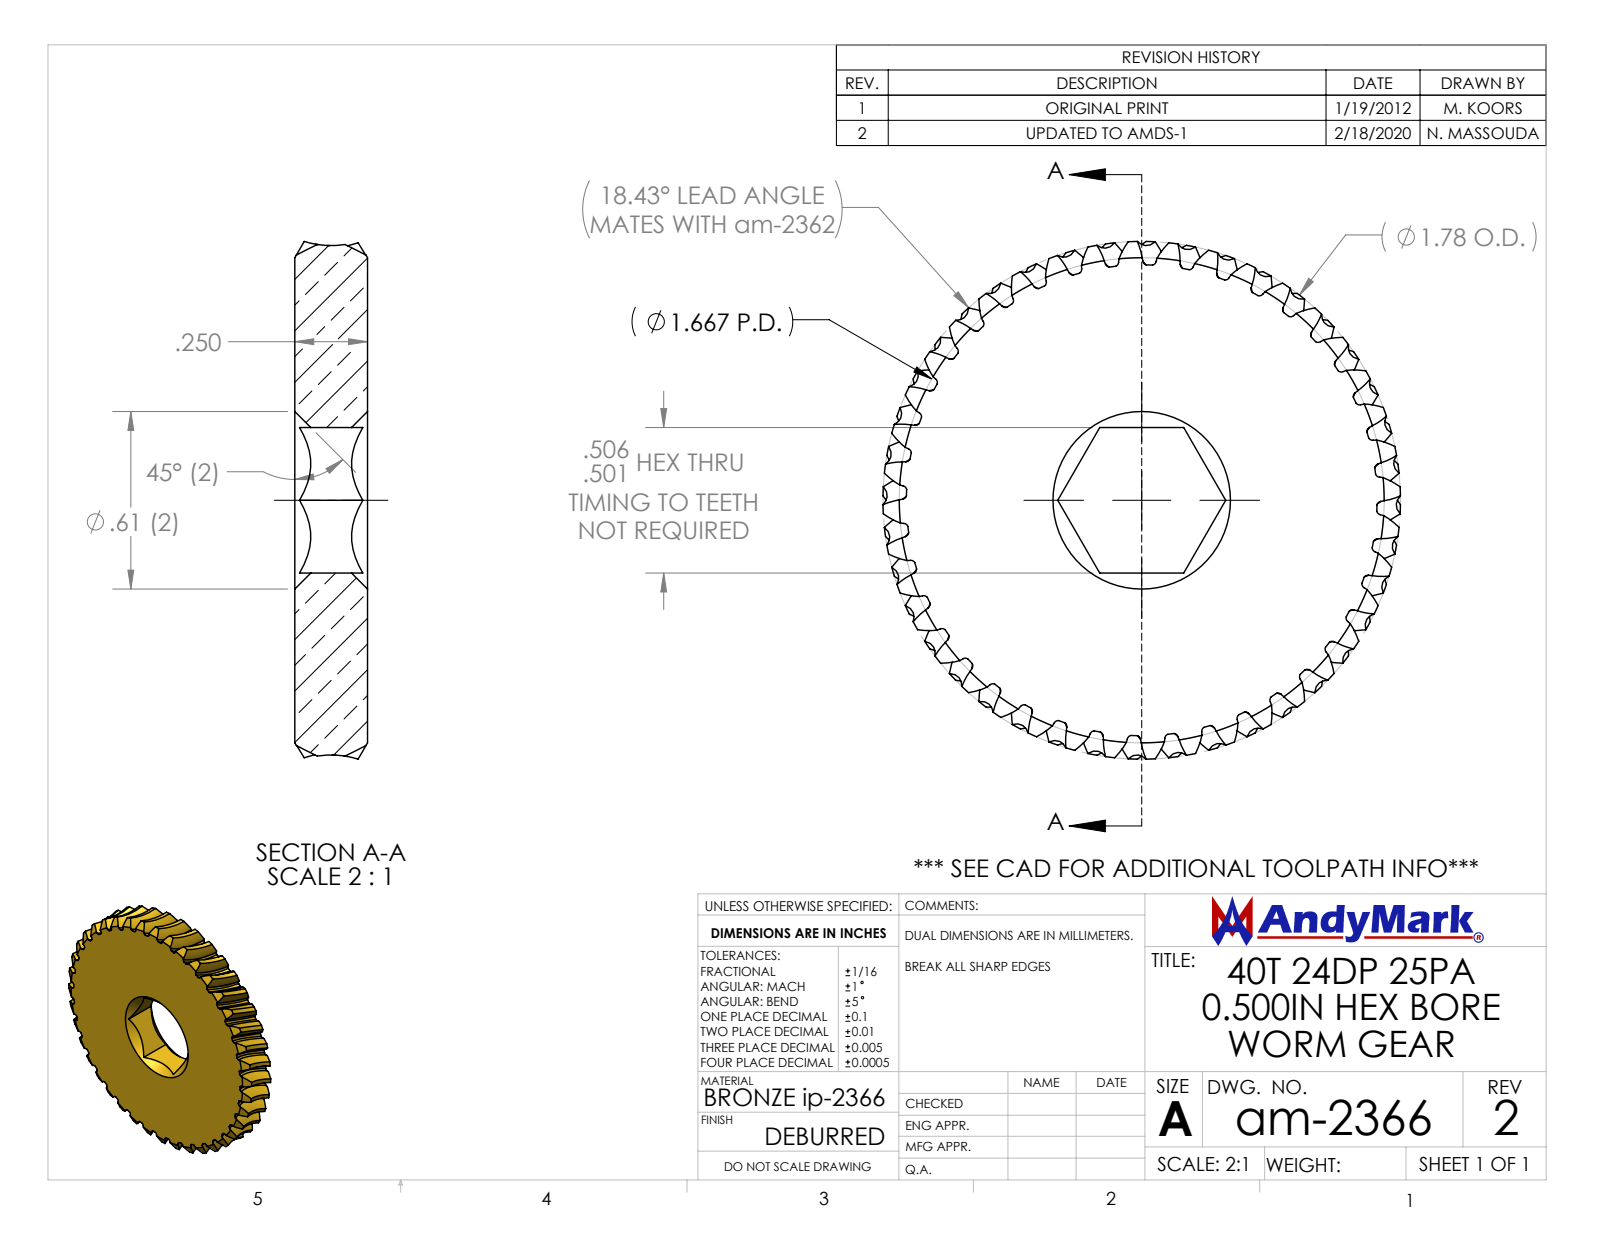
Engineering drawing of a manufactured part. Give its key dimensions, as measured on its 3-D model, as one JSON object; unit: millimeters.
{"part_name": "am-2366 40T Worm Gear 0.500in Hex Bore REV2", "step_written_by": "SolidWorks 2019 (AUTOMOTIVE_DESIGN)", "units": "millimeters", "bodies": {"solids": 1, "faces": 375, "planar": 8, "cylindrical": 0, "other": 367}, "overall_size": [45.2, 45.2, 6.4], "volume_mm3": 8050, "surface_area_mm2": 4452, "face_to_face_distances": [6.4, 12.7]}
